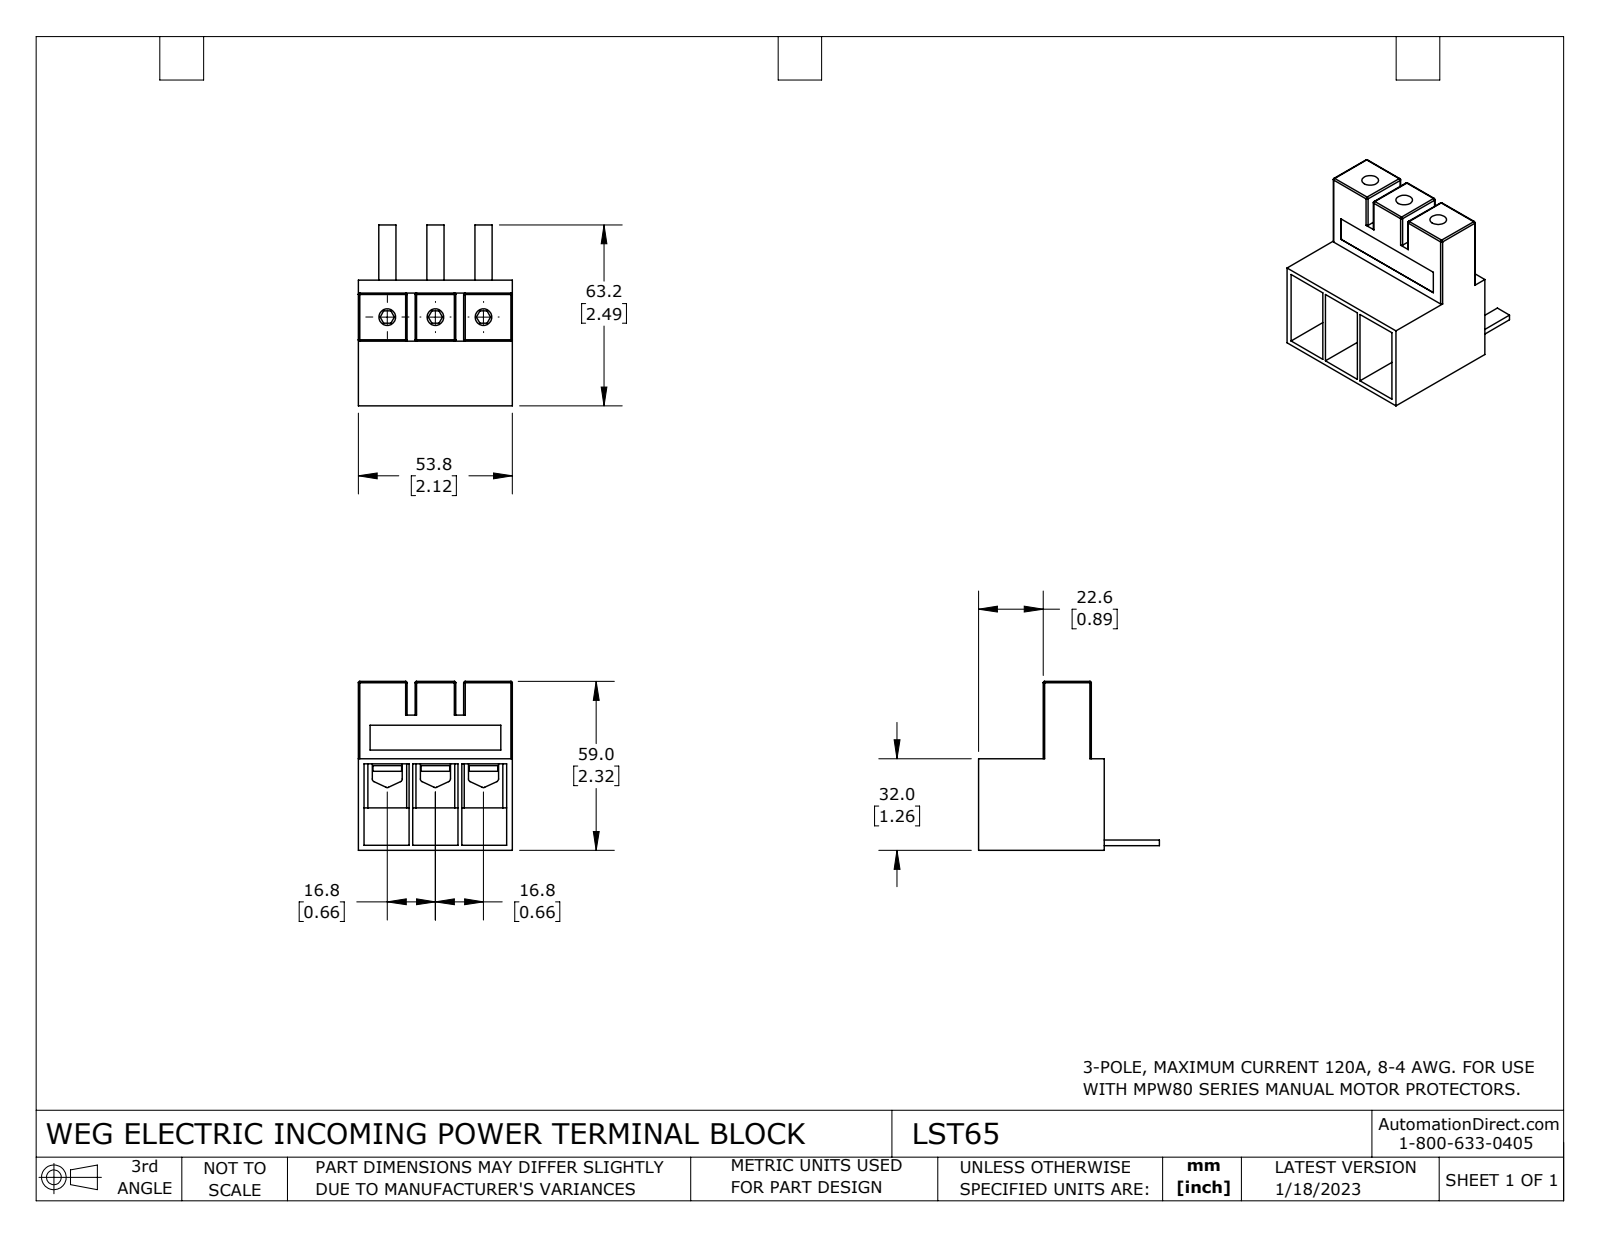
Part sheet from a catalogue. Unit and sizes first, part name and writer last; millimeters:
Units: millimetres
Overall size (bounding box): 63.2 × 59 × 53.8
Round holes (diameter × count): ⌀5.8 ×3
Round bosses / shafts (diameter × count): ⌀10 ×3, ⌀8.5 ×3
Partial cylindrical surfaces — rounded edges, fillets, slot ends (radius × count): R0.5 ×20, R1 ×17, R3 ×2
Main face-to-face distances: 2, 17.7, 17, 1.8, 15.7, 30.2, 13.5, 17.1, 19, 34.1
Hole centre spacings: 16.8, 33.6
Volume: 54 865 mm³ · Surface area: 42 828 mm²
Bodies: 10 solids, 395 faces (308 planar, 69 cylindrical, 18 other)
Part name (STEP PRODUCT): LST65
STEP written by: SolidWorks 2021 (CONFIG_CONTROL_DESIGN)
